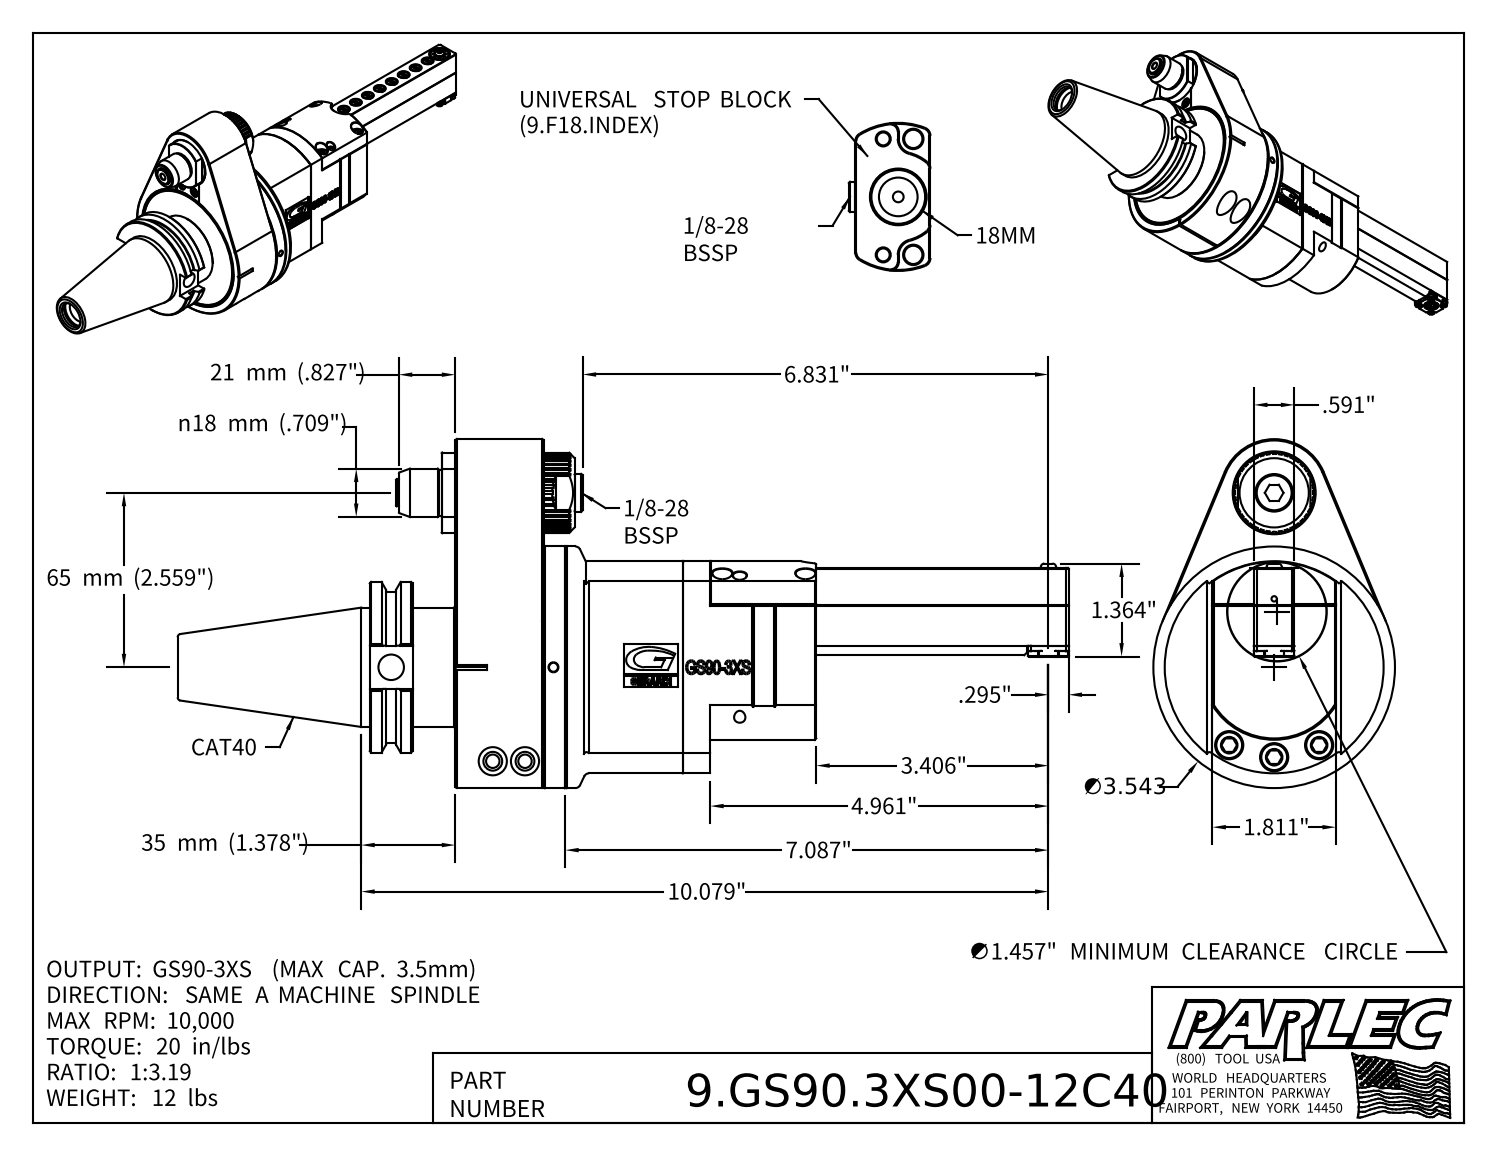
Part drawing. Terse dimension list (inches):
name: 9.GS90.3XS00-12C40; 9_GS90_3XS; 9_GA1_446_1 (Classic, Type 1, Cat40, 65mm)
written by: Autodesk Inventor 2022 (AUTOMOTIVE_DESIGN)
unit: in
bodies: 5 solids, 2071 faces (920 planar, 470 cylindrical, 681 other)
size: 13.067 × 5.118 × 3.543
volume: 38.22 in³; area: 241 in²
holes: 10× ⌀0.276, 9× ⌀0.165, 9× ⌀0.335, 8× ⌀0.047, 7× ⌀0.197, 6× ⌀0.413, 4× ⌀0.287, 3× ⌀0.13, 3× ⌀0.236, 3× ⌀0.709, 2× ⌀0.083, 2× ⌀0.157
bosses: 9× ⌀0.157, 8× ⌀0.256, 8× ⌀0.177, 5× ⌀0.394, 4× ⌀0.276, 4× ⌀0.146, 2× ⌀0.315, 2× ⌀0.079
rounds: 84× R0.01, 32× R0.039, 8× R0.246, 7× R0.079, 2× R0.085, 2× R0.118, 2× R0.167, 1× R0.092
face distances: 1.299, 1.201, 0.61, 0.591, 1.811, 0.197, 0.315, 0.118, 1.181, 0.984
hole spacings: 1.476, 0.157, 0.413, 0.827, 1.24, 2.557, 1.654, 1.98
